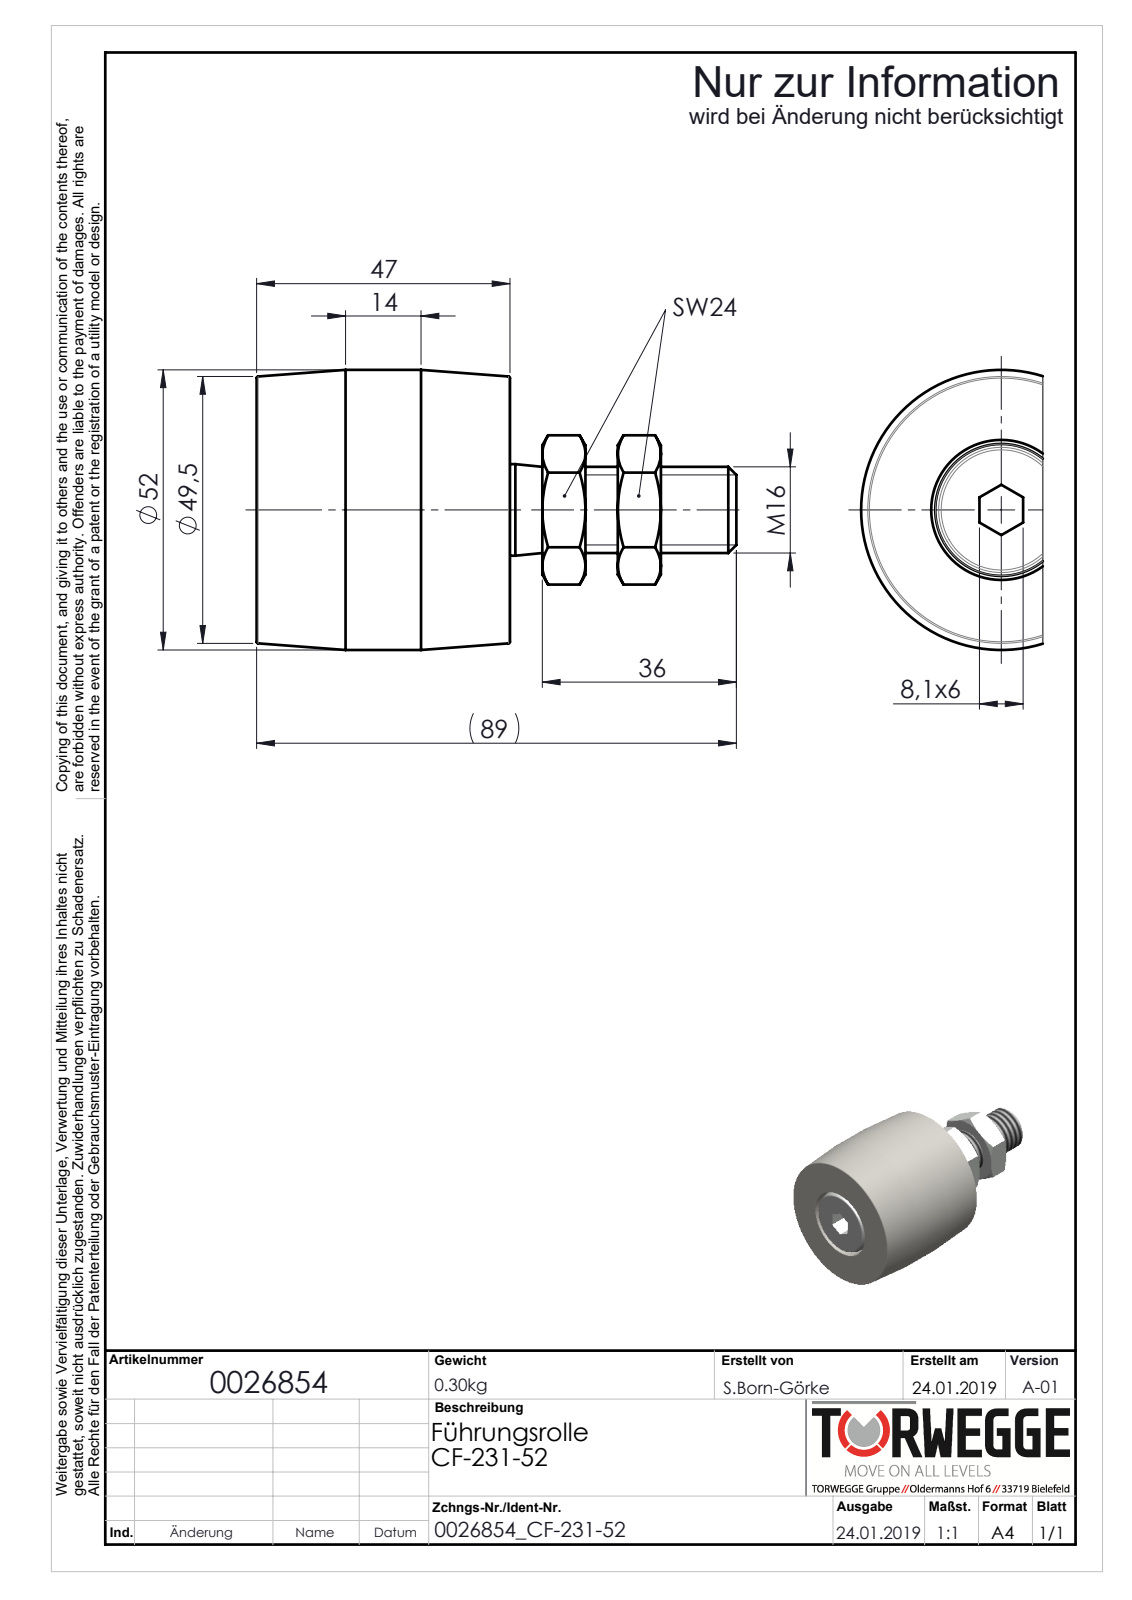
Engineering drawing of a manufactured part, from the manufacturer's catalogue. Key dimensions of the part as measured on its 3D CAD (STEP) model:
Part name (STEP PRODUCT): 0026854_CF-231-52_(A-01)
STEP written by: SolidWorks 2018 (AUTOMOTIVE_DESIGN)
Units: millimetres
Bodies: 4 solids, 101 faces (29 planar, 20 cylindrical, 52 other)
Overall size (bounding box): 89 × 52 × 52
Volume: 108 477 mm³ · Surface area: 22 657 mm²
Round holes (diameter × count): ⌀14 ×1, ⌀16 ×1, ⌀18 ×1, ⌀26 ×1
Round bosses / shafts (diameter × count): ⌀52 ×1, ⌀24.5 ×1, ⌀17 ×1
Main face-to-face distances: 47, 6, 14, 24, 41, 61, 8, 28, 22, 75
